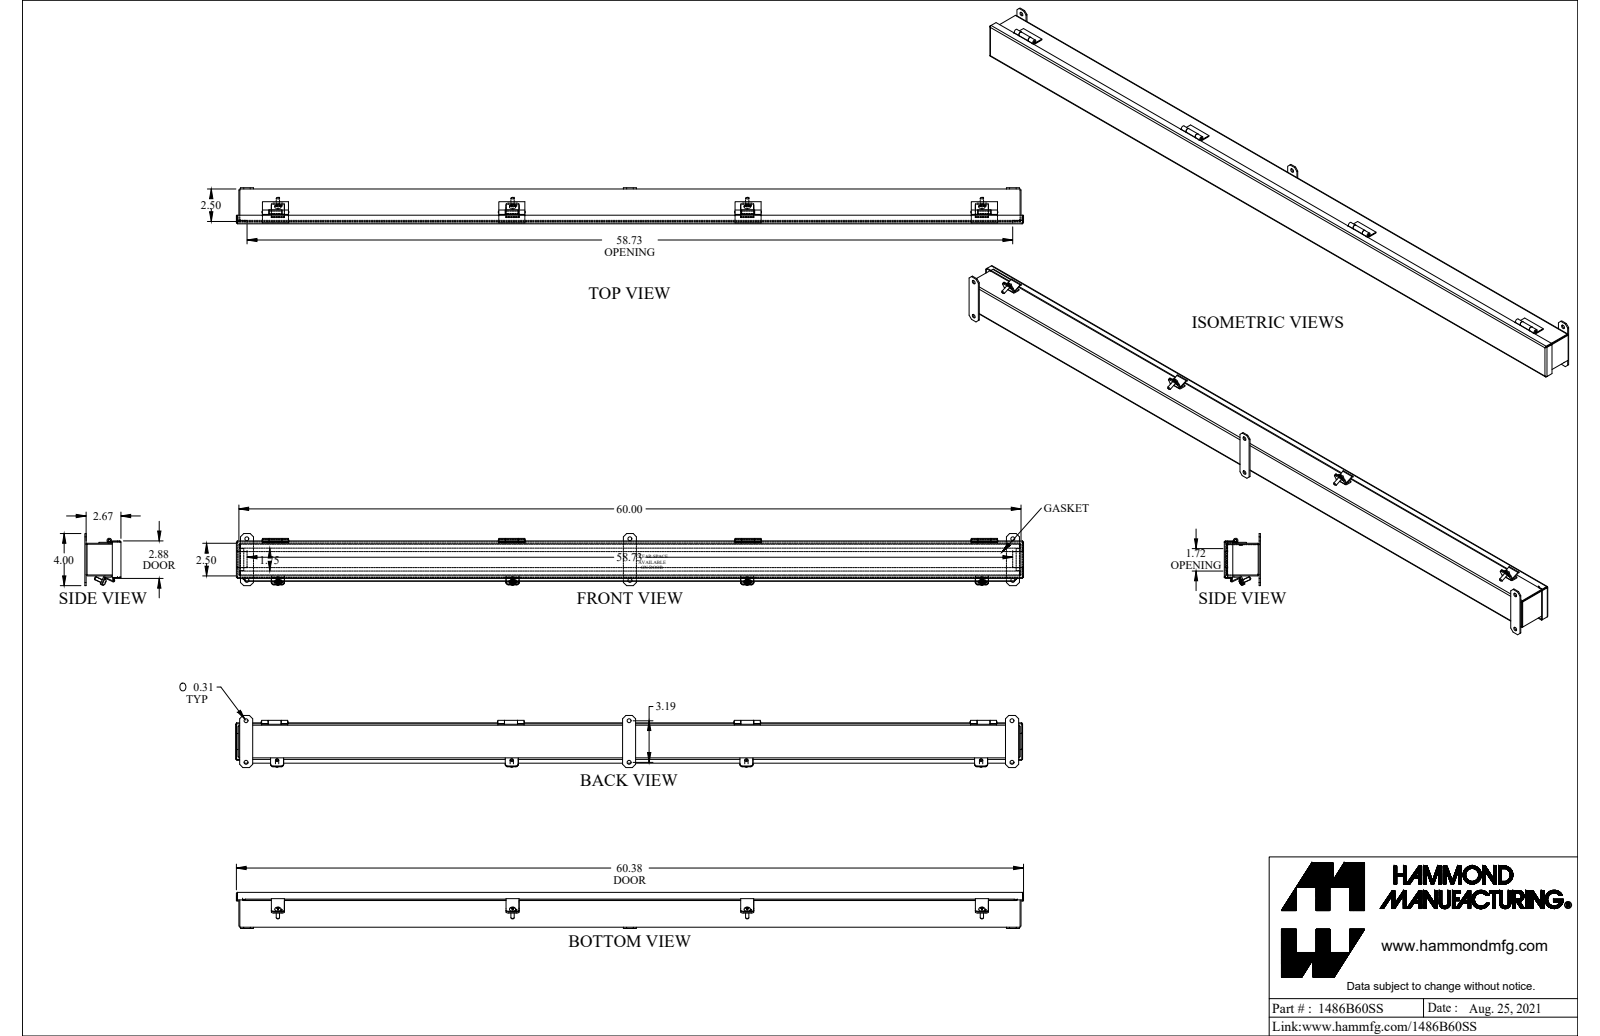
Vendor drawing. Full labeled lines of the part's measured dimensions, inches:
Part name (STEP PRODUCT): 1486B60SS
STEP written by: SolidWorks 2021 (AUTOMOTIVE_DESIGN)
Units: inches
Bodies: 16 solids, 642 faces (444 planar, 160 cylindrical, 38 other)
Overall size (bounding box): 60.375 × 4 × 2.767
Volume: 73.63 in³ · Surface area: 1 777 in²
Round holes (diameter × count): ⌀0.313 ×6, ⌀0.213 ×4, ⌀0.187 ×1
Round bosses / shafts (diameter × count): ⌀0.483 ×4, ⌀0.25 ×4, ⌀0.337 ×1, ⌀0.18 ×1
Partial cylindrical surfaces — rounded edges, fillets, slot ends (radius × count): R0.188 ×16, R0.036 ×11, R0.108 ×11, R0.01 ×8, R0.03 ×8, R0.141 ×8, R0.029 ×2, R0.086 ×2
Main face-to-face distances: 0.072, 2.428, 2.6, 0.187, 2.356, 2.5, 0.259, 2.528, 2.672, 2.615
Hole centre spacings: 3.188, 18, 29.375, 29.547, 36, 29.375, 29.548, 54
